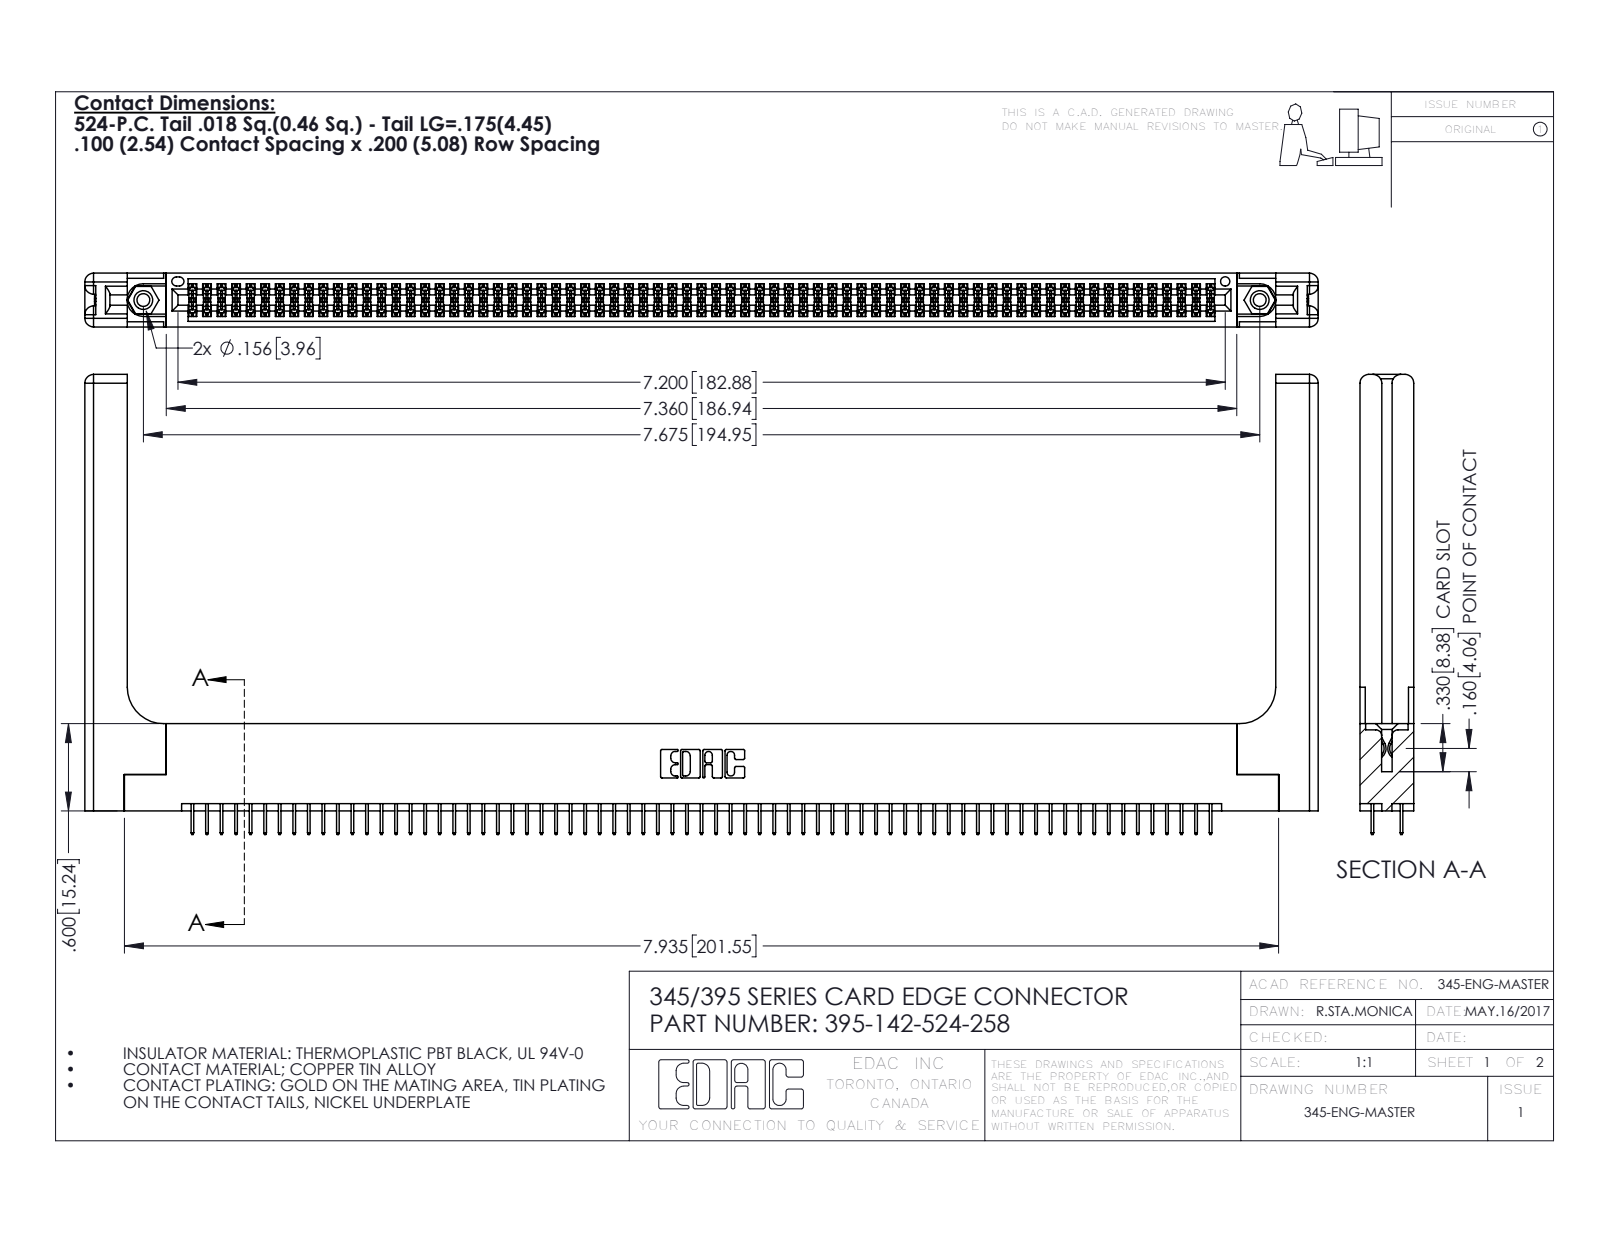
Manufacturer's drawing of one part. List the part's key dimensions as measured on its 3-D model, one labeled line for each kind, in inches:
Part name (STEP PRODUCT): 345-292-001_345-293-124; 345-250-001_345-250-001-102; 345-220-058_345-220-058; 345 Part_Flush Mounting Lugs - 0.156 Dia-TH (+1 more)
STEP written by: SolidWorks 2016 (CONFIG_CONTROL_DESIGN)
Units: inches
Bodies: 147 solids, 8050 faces (5766 planar, 2224 cylindrical, 60 other)
Overall size (bounding box): 8.479 × 3.162 × 0.37
Volume: 1.797 in³ · Surface area: 55.89 in²
Round holes (diameter × count): ⌀0.089 ×2, ⌀0.125 ×2, ⌀0.156 ×2, ⌀0.064 ×1
Round bosses / shafts (diameter × count): ⌀0.155 ×2
Partial cylindrical surfaces — rounded edges, fillets, slot ends (radius × count): R0.006 ×213, R0.01 ×22, R0.06 ×16, R0.007 ×6, R0.031 ×6, R0.026 ×3, R0.014 ×2, R0.019 ×2
Main face-to-face distances: 0.072, 0.298, 0.37, 0.2, 0.098, 0.272, 0.025, 0.225, 0.072, 0.148
Hole centre spacings: 0.27, 7.439, 7.675
